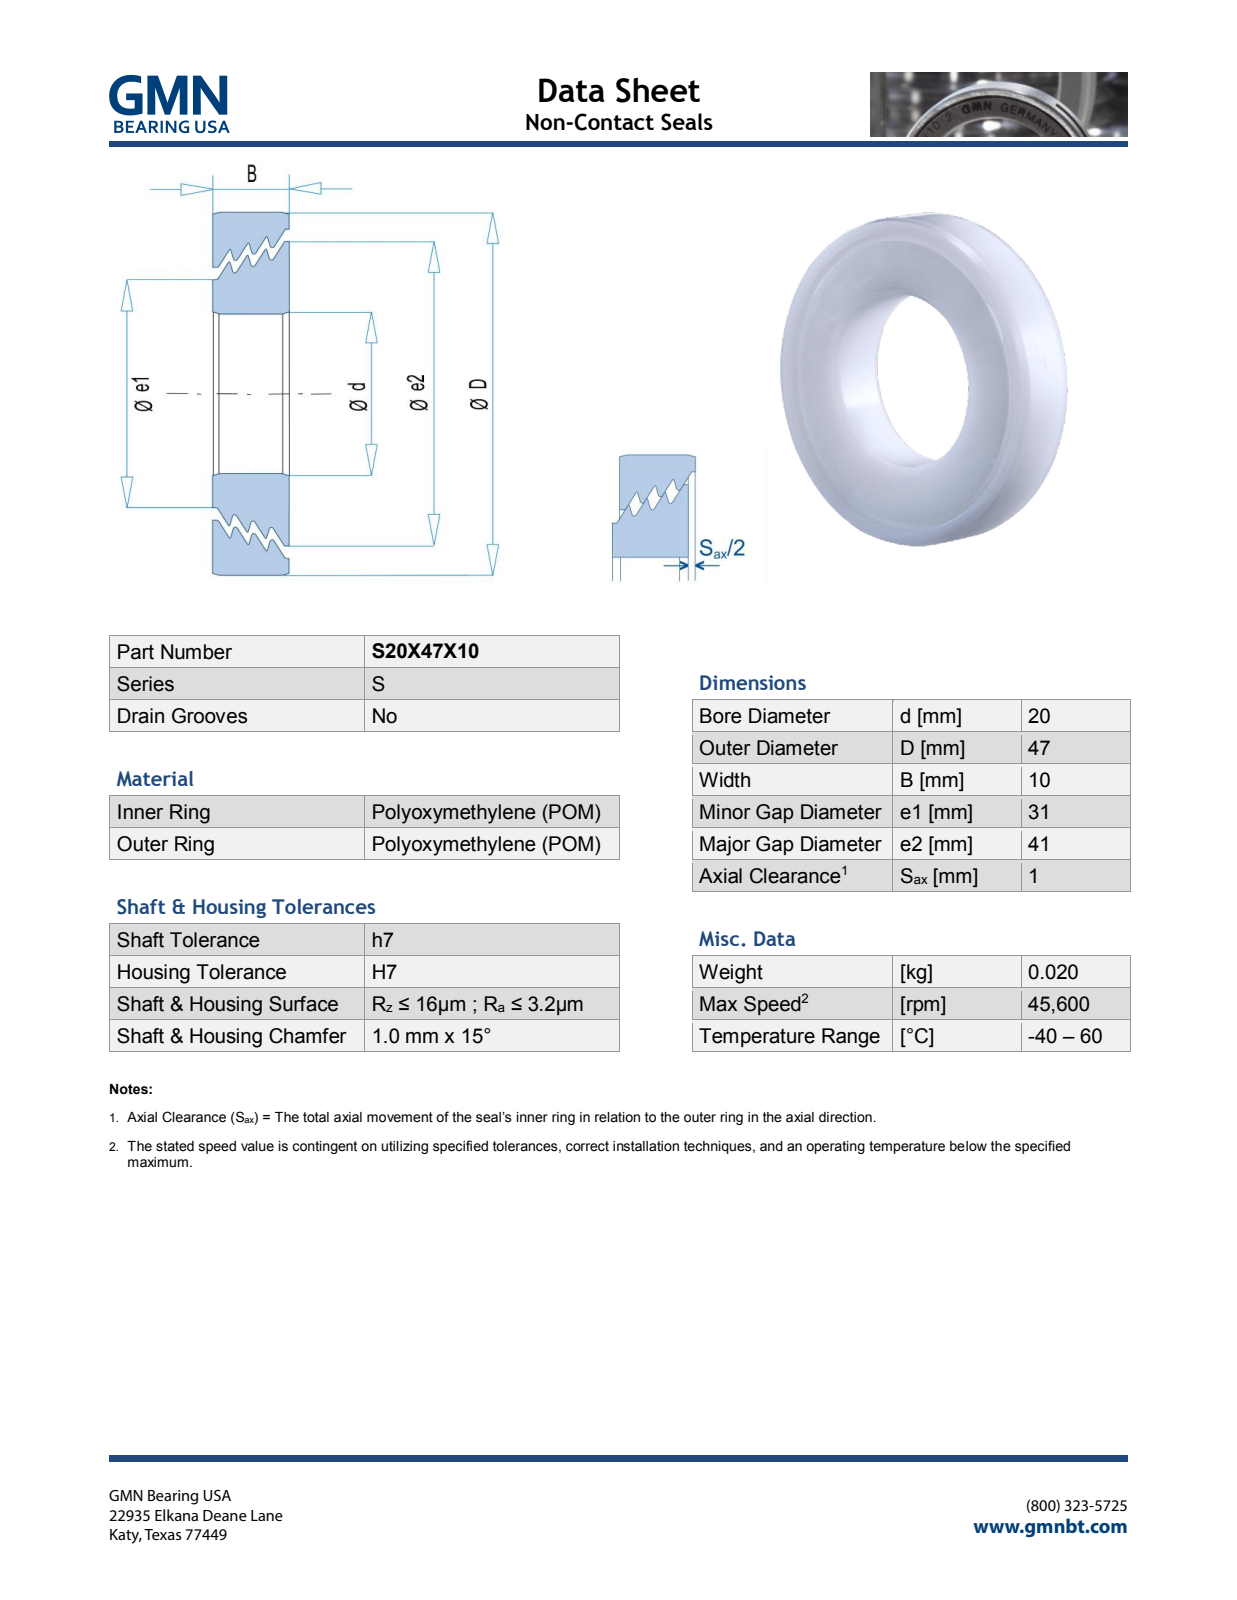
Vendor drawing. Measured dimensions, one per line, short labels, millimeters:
name: S20X47X10_PRT
written by: PRO/ENGINEER BY PARAMETRIC TECHNOLOGY CORPORATION, 2013150 (AUTOMOTIVE_DESIGN)
unit: mm
bodies: 2 solids, 592 faces (512 planar, 12 cylindrical, 68 other)
size: 47 × 47 × 10.07
volume: 13 212 mm³; area: 9 451 mm²
holes: 1× ⌀20, 1× ⌀32.63, 1× ⌀42.63
bosses: 1× ⌀47, 1× ⌀41, 1× ⌀31
face distances: 10, 10.07, 0.36, 2.88, 0.37, 2.52, 2.04, 0.33, 2.51, 2.4
